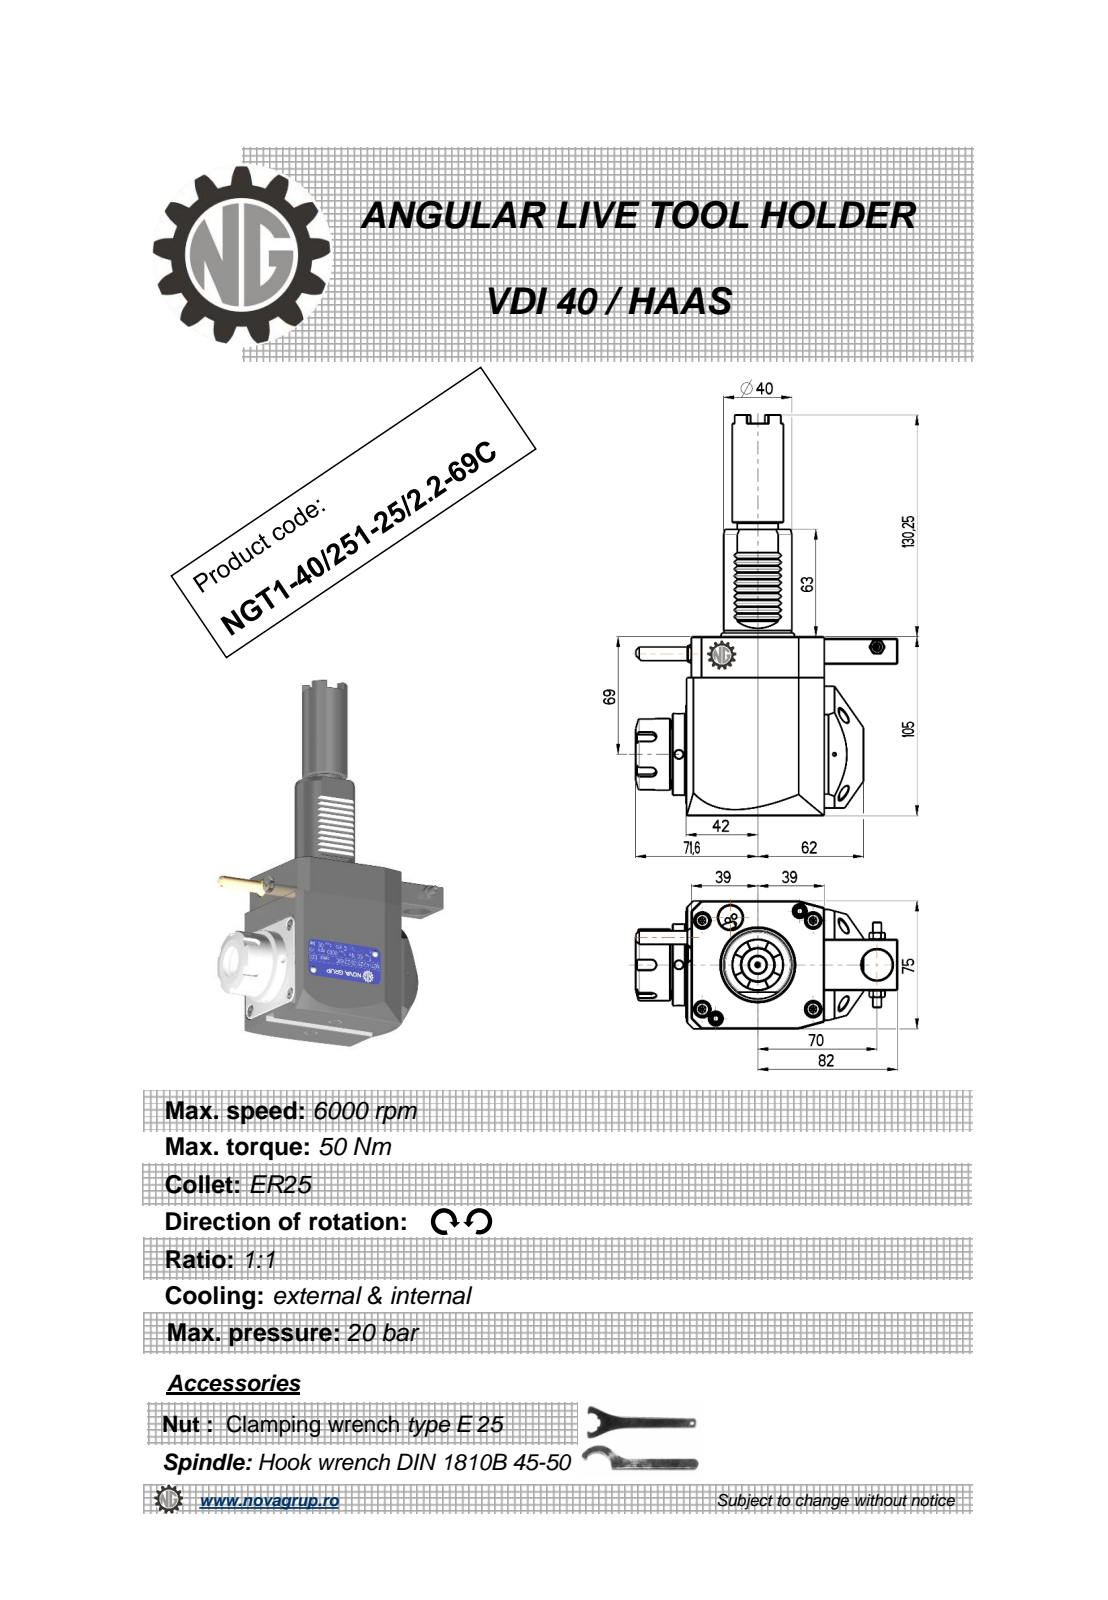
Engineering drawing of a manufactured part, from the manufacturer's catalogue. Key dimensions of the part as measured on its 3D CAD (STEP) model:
Part name (STEP PRODUCT): NGT1_40_251_25_2_2_69C
STEP written by: PRO/ENGINEER BY PARAMETRIC TECHNOLOGY CORPORATION, 2010280 (CONFIG_CONTROL_DESIGN)
Units: millimetres
Bodies: 1 solid, 482 faces (227 planar, 92 cylindrical, 163 other)
Overall size (bounding box): 235.25 × 153.6 × 76.6
Volume: 856 630 mm³ · Surface area: 75 799 mm²
Round holes (diameter × count): ⌀5 ×3, ⌀3 ×1, ⌀4.2 ×1, ⌀9.5 ×1, ⌀18 ×1, ⌀19.5 ×1, ⌀20.3 ×1
Round bosses / shafts (diameter × count): ⌀48 ×1, ⌀42 ×1, ⌀40 ×1, ⌀37.5 ×1, ⌀33 ×1, ⌀30 ×1, ⌀24 ×1, ⌀10 ×1
Partial cylindrical surfaces — rounded edges, fillets, slot ends (radius × count): R0.26 ×12, R0.3 ×10, R0.2 ×6, R3 ×5, R0.5 ×1, R40 ×1
Main face-to-face distances: 75, 105, 81, 104, 89, 80.8, 1, 101, 3, 2.8
Hole centre spacings: 16.19, 46.25, 61.13, 61.5, 70, 116.25, 132.22
